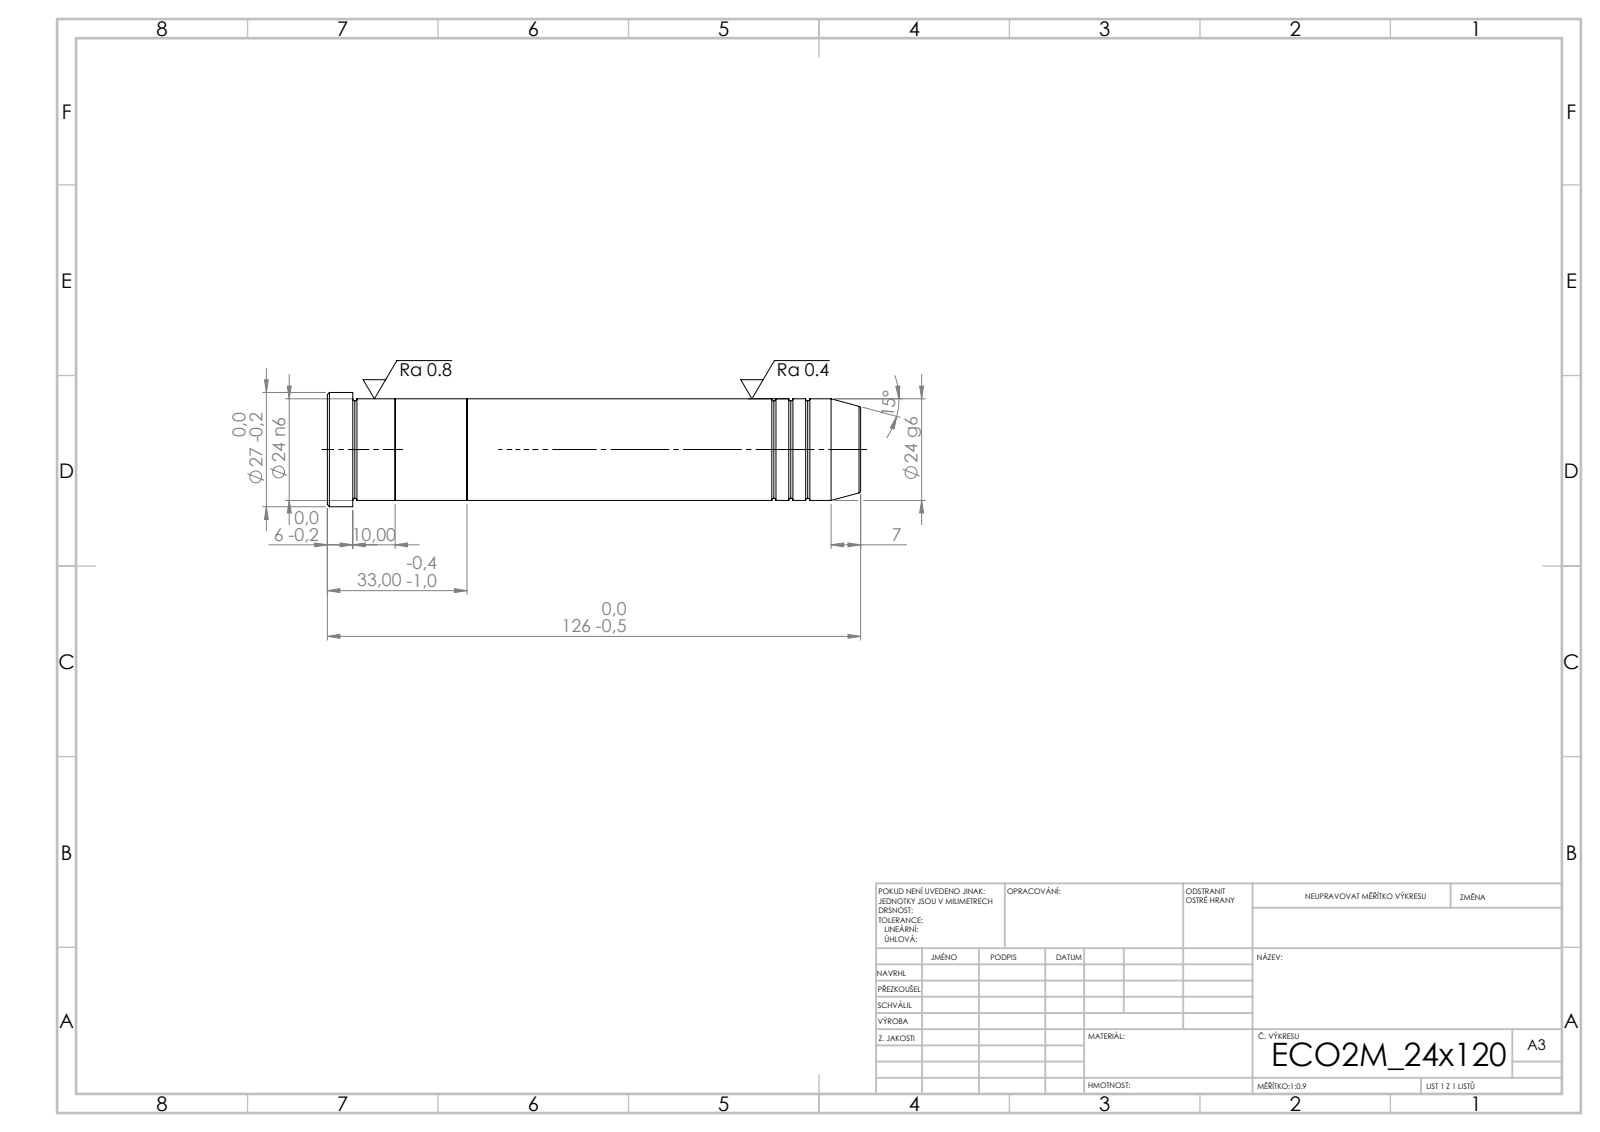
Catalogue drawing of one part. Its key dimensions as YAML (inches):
step_written_by: "SolidWorks 2019 (CONFIG_CONTROL_DESIGN)"
units: inches
bodies: {solids: 3, faces: 43, planar: 7, cylindrical: 14, other: 22}
overall_size: [4.961, 1.063, 1.063]
volume: 3.486
surface_area: 19.35
round_bosses_or_shafts:
  - {diameter: 1.063, count: 1}
  - {diameter: 0.945, count: 1}
face_to_face_distances: [0.669, 1.299, 0.63, 3.661, 4.331, 4.961, 4.724, 1.063, 0.394, 0.236]
